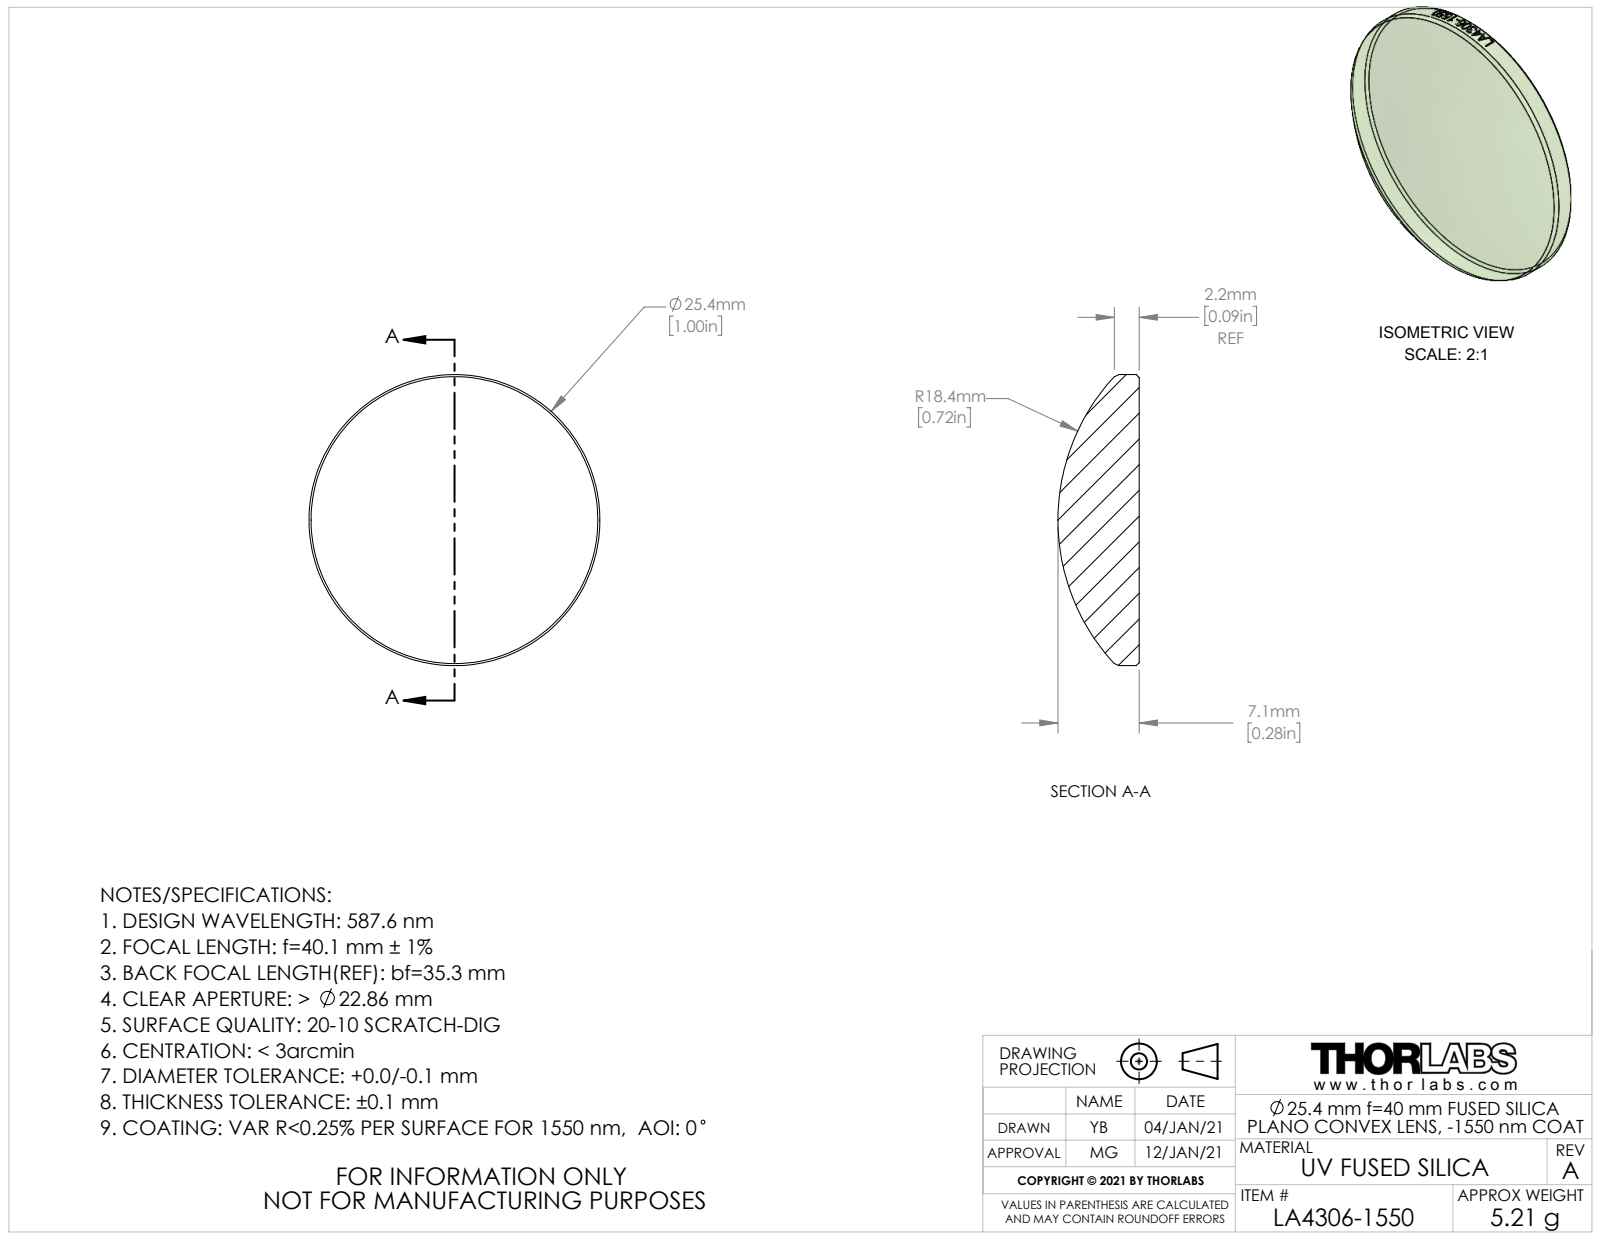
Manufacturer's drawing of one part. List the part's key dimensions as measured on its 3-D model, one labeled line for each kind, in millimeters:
Part name (STEP PRODUCT): CTN015951-E0W
STEP written by: SolidWorks 2018 (AUTOMOTIVE_DESIGN)
Units: millimetres
Bodies: 1 solid, 25 faces (1 planar, 18 cylindrical, 6 other)
Overall size (bounding box): 25.4 × 25.4 × 7.1
Volume: 2 360 mm³ · Surface area: 1 239 mm²
Round bosses / shafts (diameter × count): ⌀25.4 ×1
